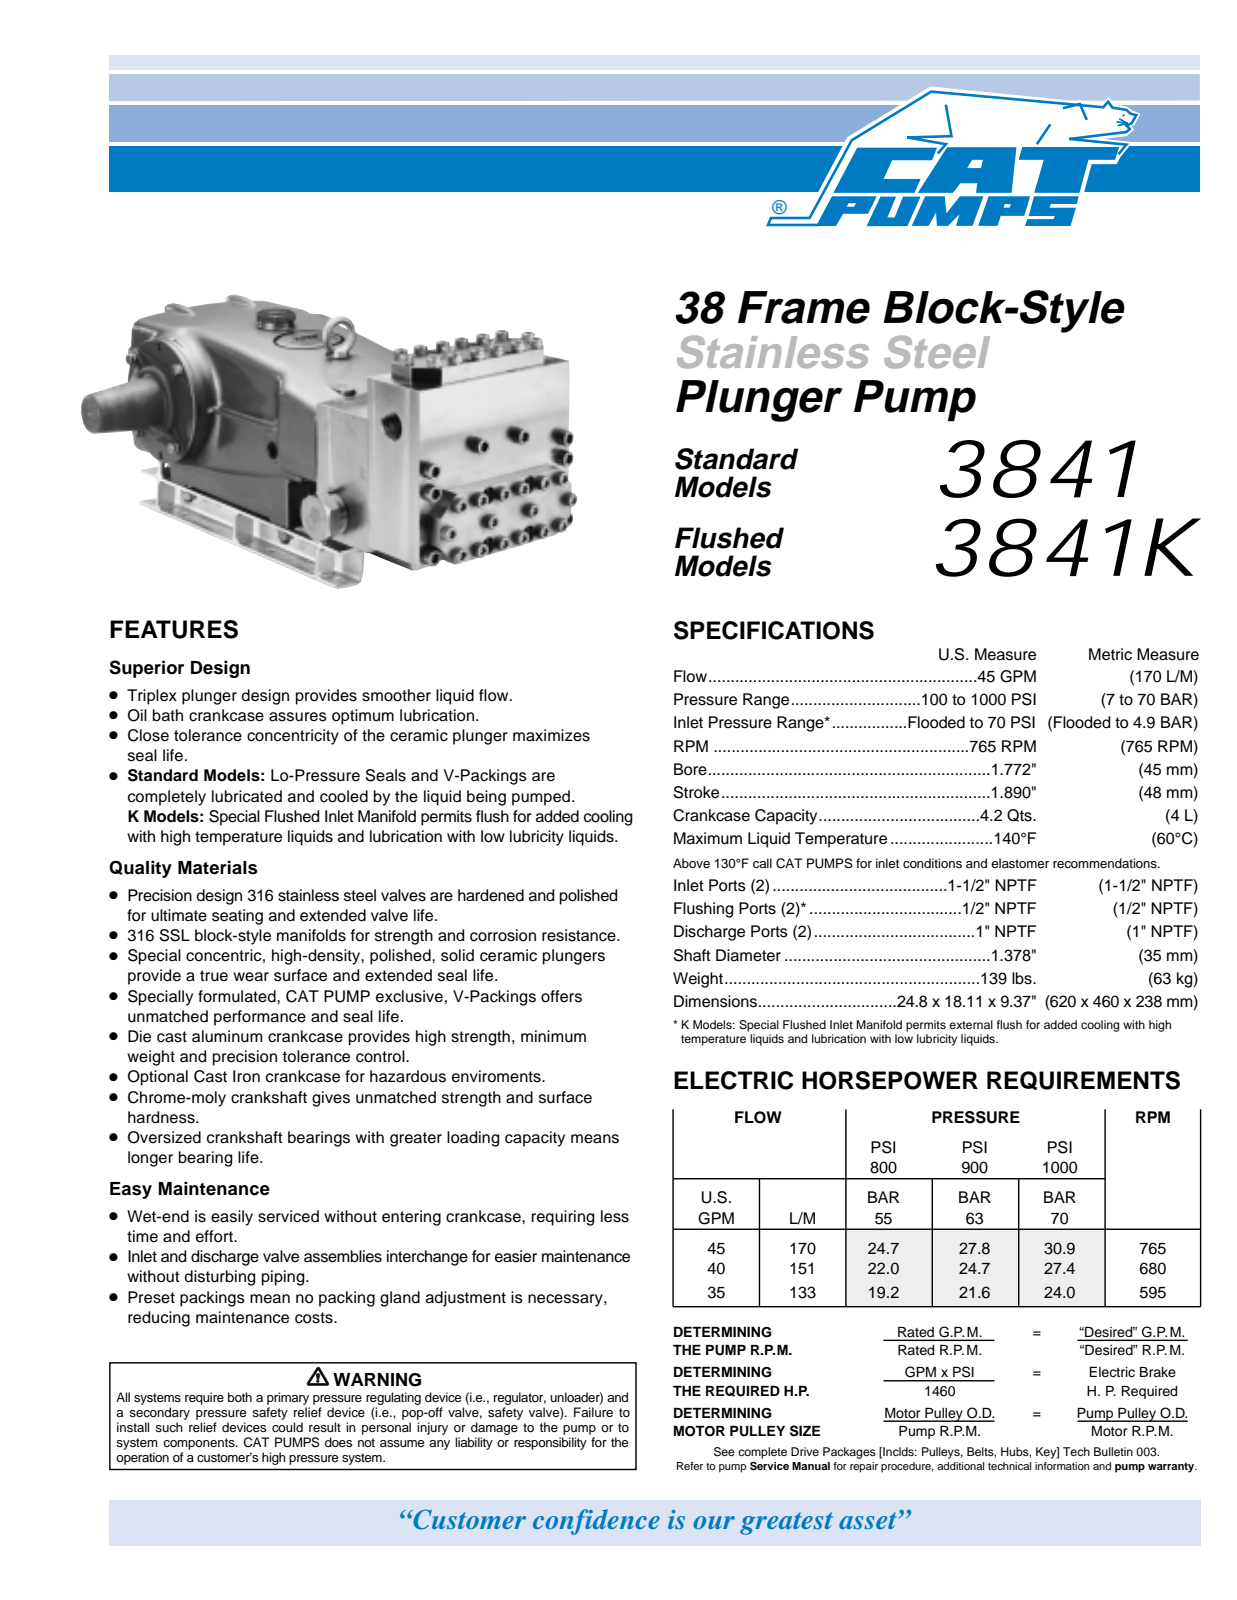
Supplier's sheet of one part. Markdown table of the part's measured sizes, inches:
| quantity | value |
| --- | --- |
| part name | 3841 |
| STEP written by | SolidWorks 2020 (CONFIG_CONTROL_DESIGN) |
| units | inches |
| bodies | 0 solids, 2359 faces (954 planar, 473 cylindrical, 932 other) |
| overall size | 24.843 × 18.11 × 9.882 |
| round holes (diameter × count) | 0.433 × 8, 0.726 × 8, 0.33 × 4, 0.466 × 4, 0.451 × 3, 0.266 × 1, 0.34 × 1, 0.591 × 1, 1.141 × 1, 1.417 × 1, 1.732 × 1, 1.937 × 1 |
| round bosses / shafts (diameter × count) | 0.63 × 32, 0.709 × 10, 0.61 × 8, 0.606 × 8, 0.827 × 4, 0.724 × 4, 1.772 × 2, 0.48 × 2 |
| partial cylindrical surfaces (radius × count) | 0.079 × 41, 0.118 × 25, 0.059 × 14, 0.394 × 13, 0.157 × 10, 0.197 × 10, 0.63 × 10, 0.039 × 7 |
| main face-to-face distances | 3.346, 0.315, 3.543, 6.89, 9.459, 0.404, 9.055, 0.719, 9.774, 10.177 |
| hole center spacings | 2.441, 2.205, 2.717, 3.045, 3.289, 4.226, 4.643, 4.784 |
